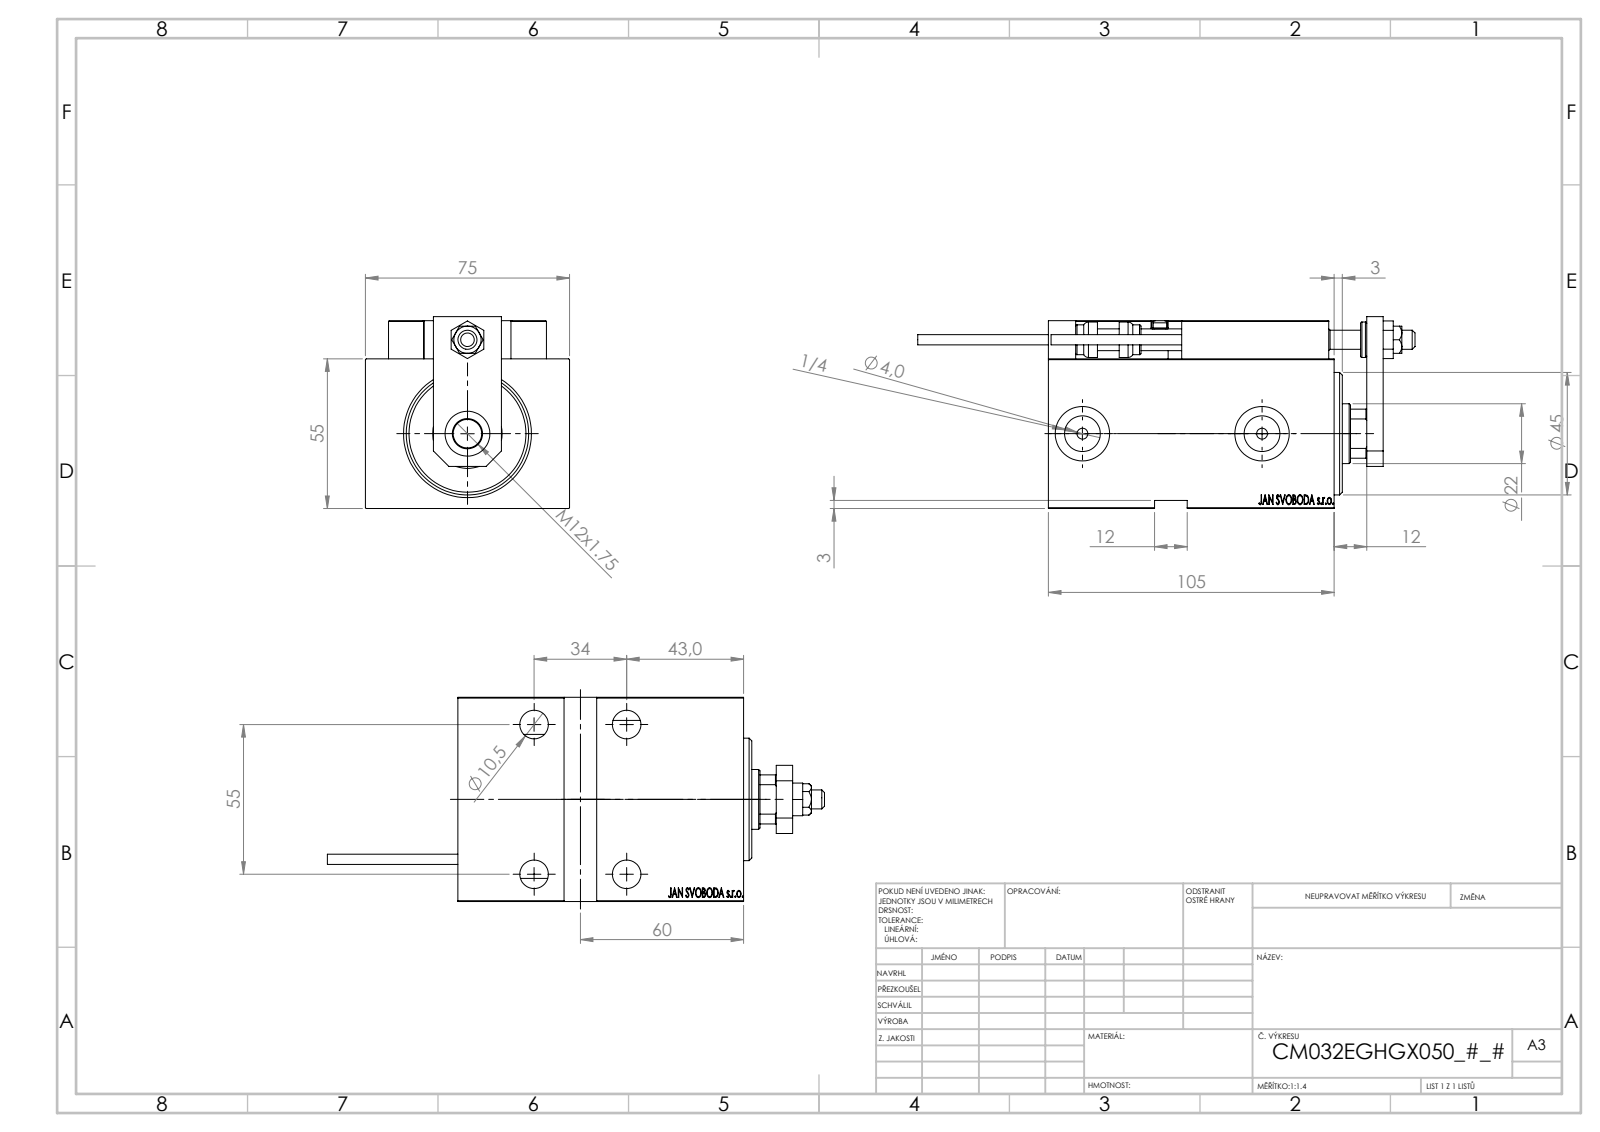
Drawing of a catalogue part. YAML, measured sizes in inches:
part_name: "V450CM_E_Body; V450CM_E_VCP; Block; ALLEN BOLT D5 (+8 more)"
step_written_by: "SolidWorks 2019 (CONFIG_CONTROL_DESIGN)"
units: inches
bodies: {solids: 24, faces: 1293, planar: 570, cylindrical: 182, other: 541}
overall_size: [7.193, 2.953, 2.776]
volume: 26.17
surface_area: 149.1
round_holes:
  - {diameter: 0.157, count: 6}
  - {diameter: 0.315, count: 5}
  - {diameter: 0.413, count: 5}
  - {diameter: 0.65, count: 5}
  - {diameter: 0.126, count: 4}
  - {diameter: 0.197, count: 2}
  - {diameter: 0.518, count: 2}
  - {diameter: 0.787, count: 2}
  - {diameter: 0.276, count: 1}
  - {diameter: 0.866, count: 1}
  - {diameter: 1.004, count: 1}
  - {diameter: 1.26, count: 1}
round_bosses_or_shafts:
  - {diameter: 0.197, count: 2}
  - {diameter: 0.15, count: 2}
  - {diameter: 0.512, count: 1}
  - {diameter: 0.433, count: 1}
partial_cylinders:
  - {radius: 0.012, count: 30}
  - {radius: 0.118, count: 2}
  - {radius: 0.413, count: 1}
face_to_face_distances: [2.165, 2.953, 0.394, 0.118, 0.551, 2.717, 4.134, 0.472, 3.74, 0.197]
hole_center_spacings: [0.448, 0.787, 1.138, 1.165, 1.169, 1.339, 1.42, 1.576]
